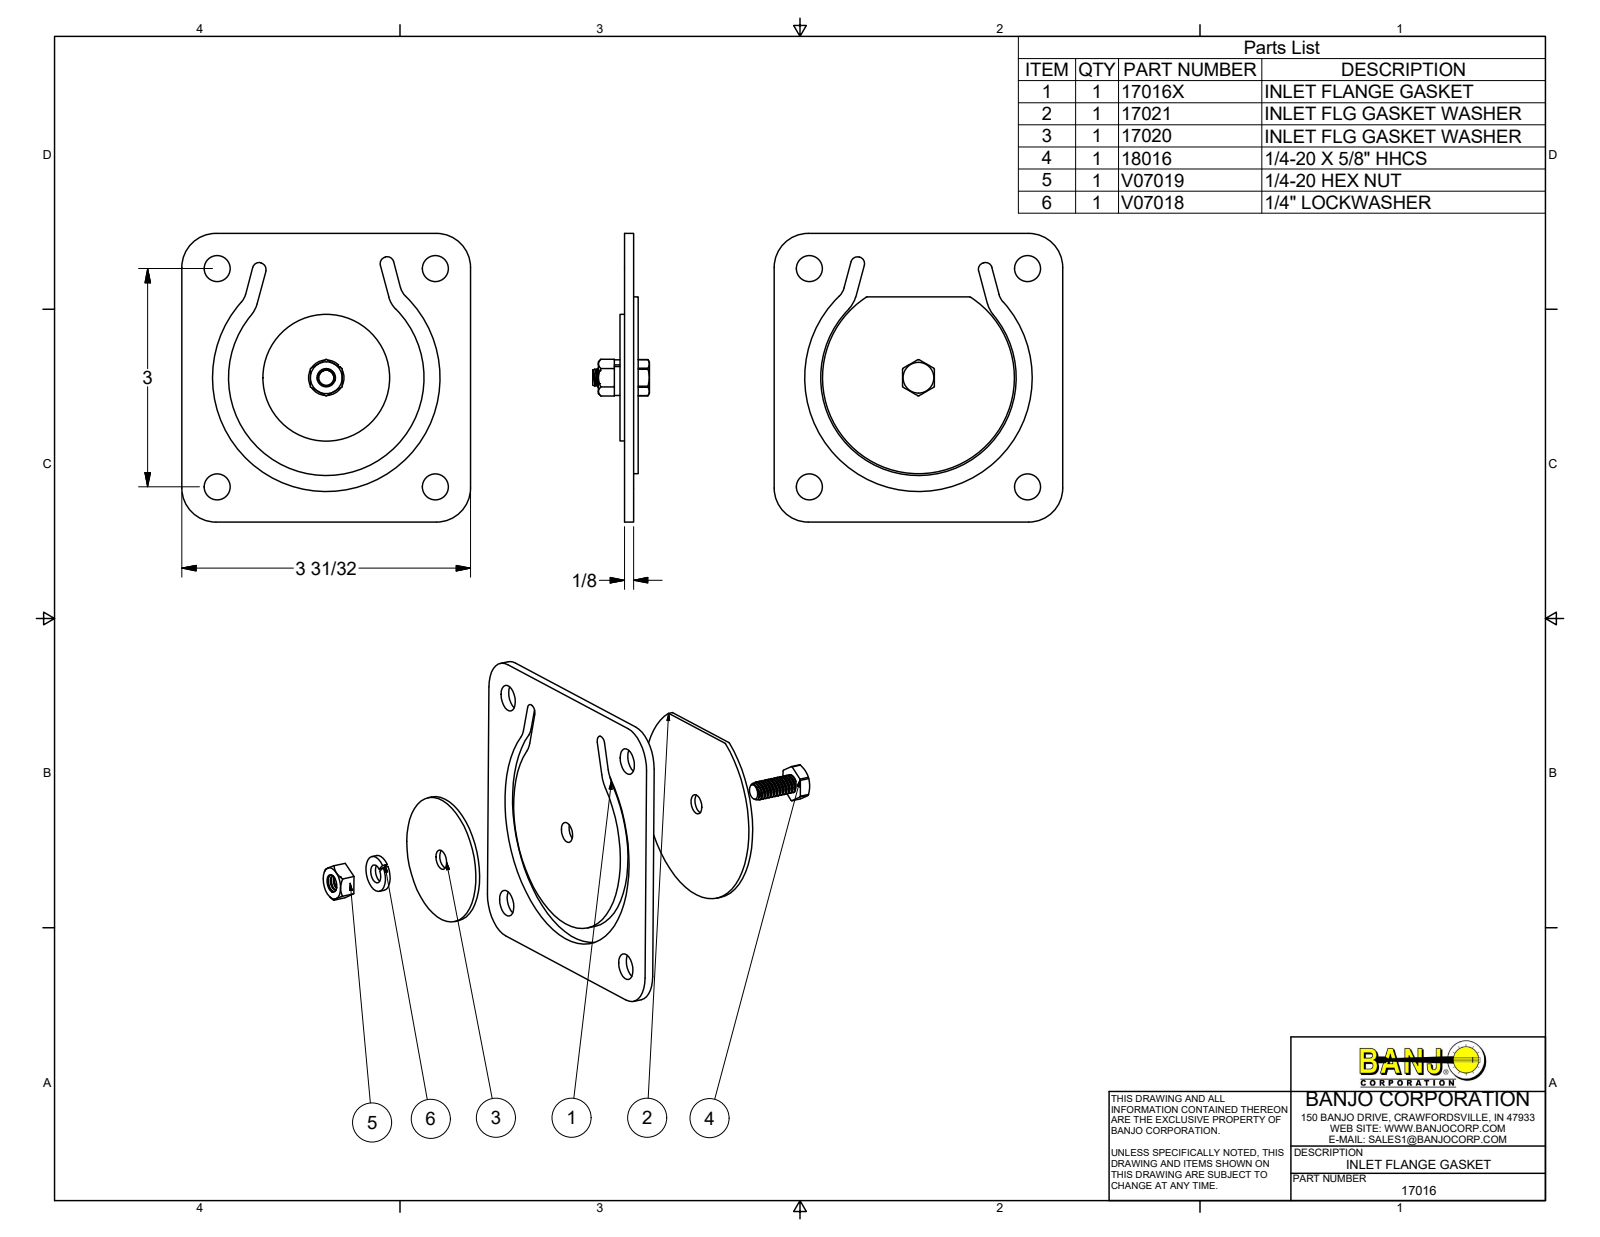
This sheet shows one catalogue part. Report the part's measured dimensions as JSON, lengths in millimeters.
{"part_name": "17016X; 17021; 17020; 18016 (+3 more)", "step_written_by": "Autodesk Inventor 2014 (AUTOMOTIVE_DESIGN)", "units": "millimeters", "bodies": {"solids": 6, "faces": 226, "planar": 38, "cylindrical": 103, "other": 85}, "overall_size": [100.81, 100.81, 19.84], "volume_mm3": 36572, "surface_area_mm2": 32152, "round_holes": [[9.13, 4], [4.98, 1], [6.4, 1], [6.86, 1], [7.14, 1]], "round_bosses_or_shafts": [[5.39, 12], [67.06, 1], [44.2, 1], [12.42, 1], [6.35, 1]], "partial_cylinders_radius": [[2.29, 4], [11.91, 4], [0.76, 2], [6.35, 2], [9.53, 2], [2.69, 1], [6.29, 1], [34.13, 1]], "face_to_face_distances": [3.17, 4.76, 1.59, 6.35, 100.8, 11.12, 1.95, 3.54, 6.71, 8.3], "hole_center_spacings": [53.88, 76.2, 107.76]}
